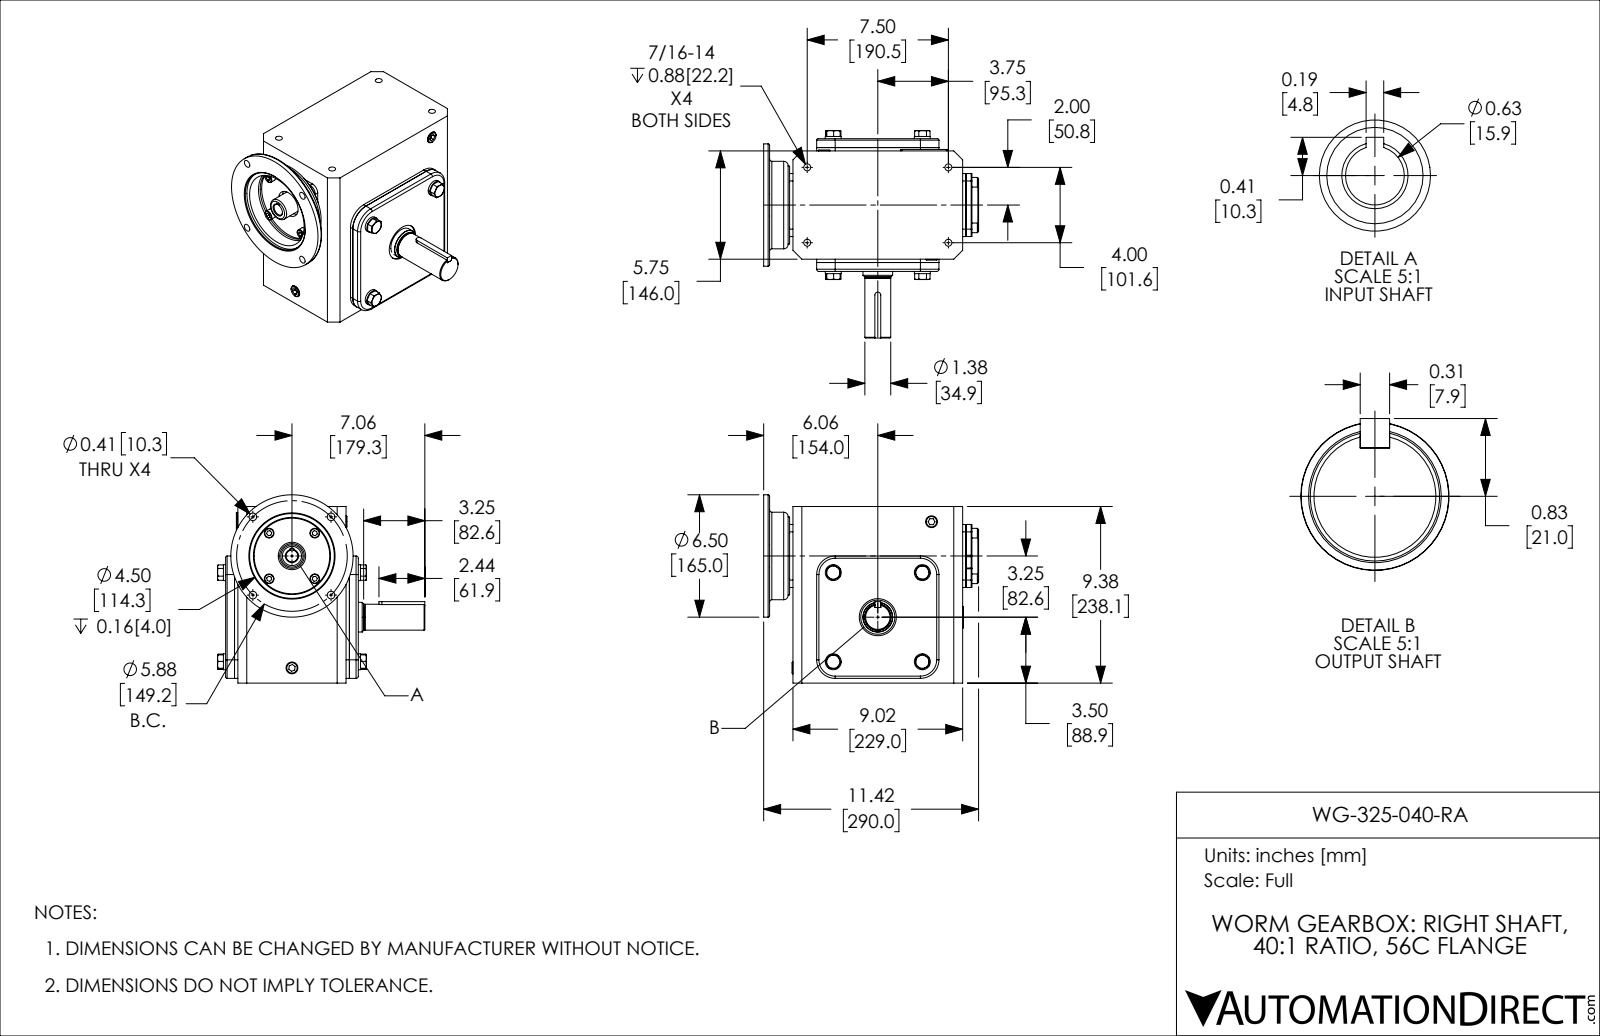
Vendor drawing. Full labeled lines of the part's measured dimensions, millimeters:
Part name (STEP PRODUCT): WG-325-040-RA
STEP written by: SolidWorks 2017 (AUTOMOTIVE_DESIGN)
Units: millimetres
Bodies: 39 solids, 576 faces (318 planar, 168 cylindrical, 90 other)
Overall size (bounding box): 290 × 279.8 × 253.9
Volume: 8 251 000 mm³ · Surface area: 578 800 mm²
Round holes (diameter × count): ⌀9.3 ×4, ⌀10.3 ×4, ⌀16 ×3, ⌀15 ×1, ⌀15.9 ×1, ⌀24.8 ×1, ⌀30 ×1, ⌀37 ×1, ⌀50 ×1, ⌀62 ×1, ⌀70 ×1, ⌀102 ×1
Round bosses / shafts (diameter × count): ⌀21.5 ×4, ⌀13 ×4, ⌀165 ×1, ⌀118 ×1, ⌀105 ×1, ⌀72 ×1, ⌀40 ×1, ⌀34.9 ×1
Partial cylindrical surfaces — rounded edges, fillets, slot ends (radius × count): R2 ×11, R3 ×4, R10 ×4, R23 ×4, R25 ×4, R0.5 ×2, R1 ×2, R4 ×1
Main face-to-face distances: 2, 4.5, 165, 10, 177, 12, 167, 162.5, 14.5, 16.5
Hole centre spacings: 74.6, 105.5, 60.6, 101.6, 111.5, 145.2, 147.8, 149.2
